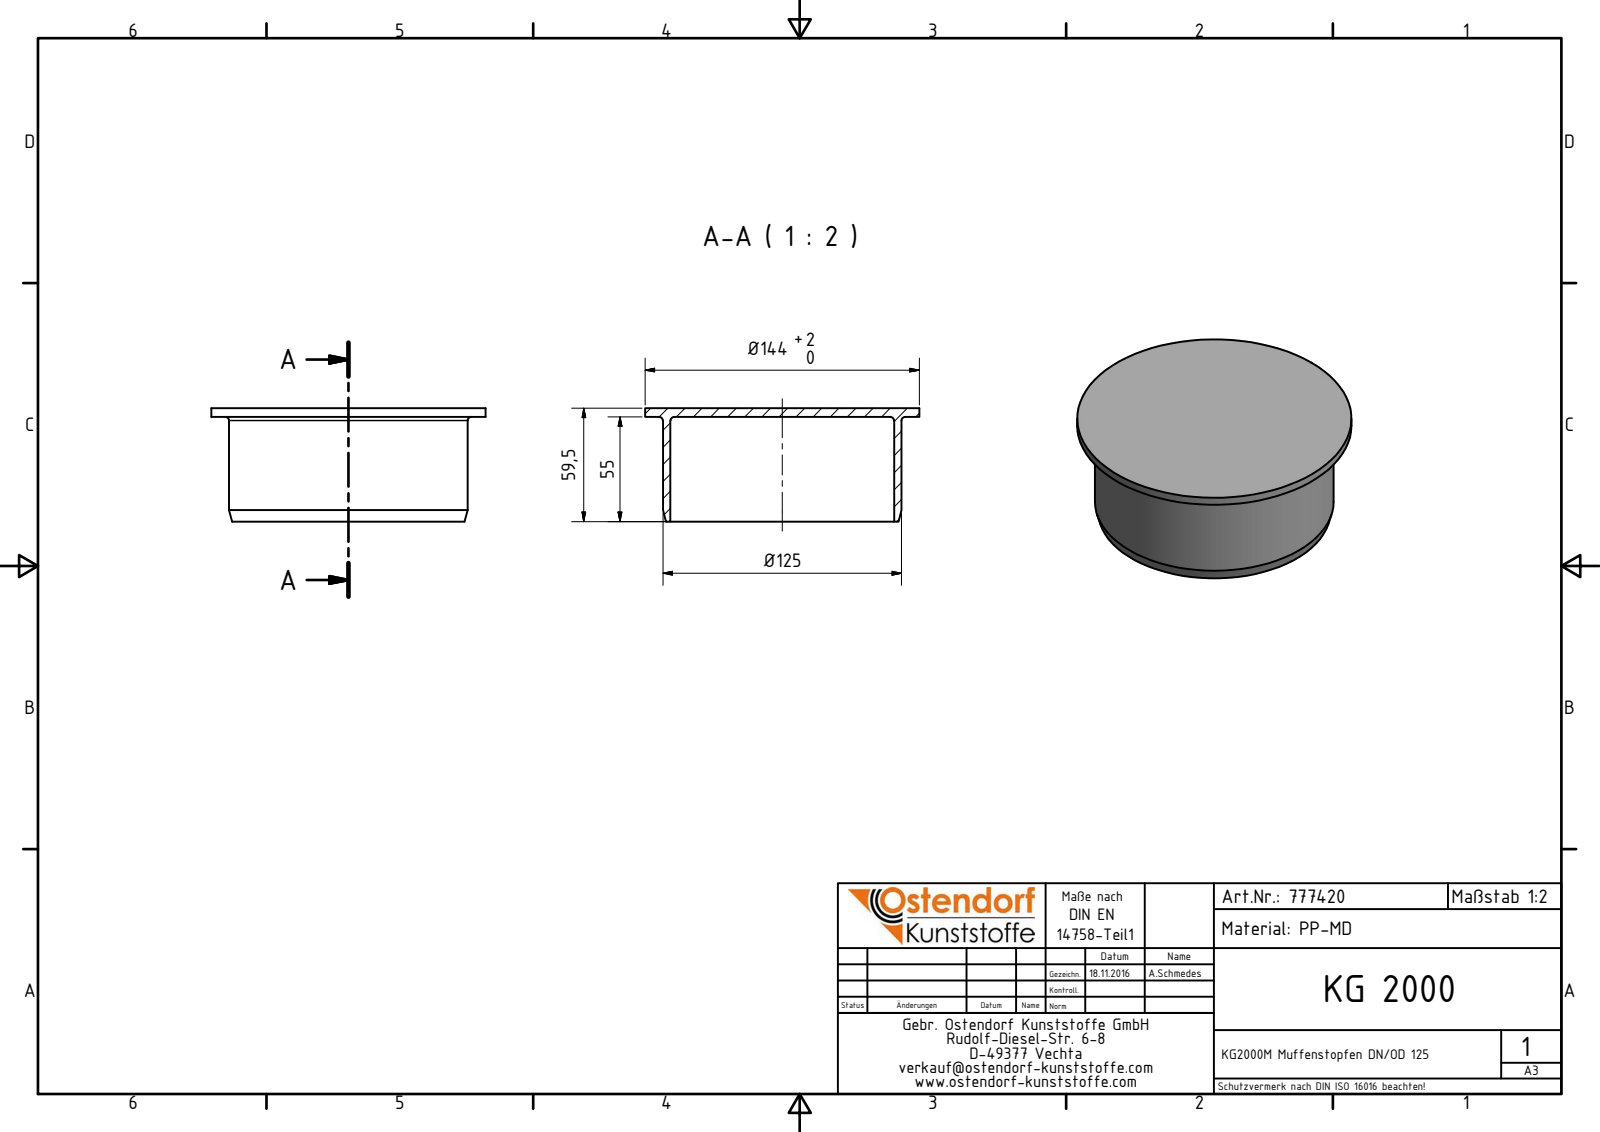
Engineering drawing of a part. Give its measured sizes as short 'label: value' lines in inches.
name: 777420 KG2000M Muffenstopfen DN_OD 125
written by: Autodesk Inventor 2016 (AUTOMOTIVE_DESIGN)
unit: in
bodies: 1 solid, 10 faces (4 planar, 3 cylindrical, 3 other)
size: 5.669 × 5.669 × 2.343
volume: 9.39 in³; area: 116.8 in²
holes: 1× ⌀4.626
bosses: 1× ⌀5.669, 1× ⌀4.933
face distances: 0.177, 2.165, 2.343
